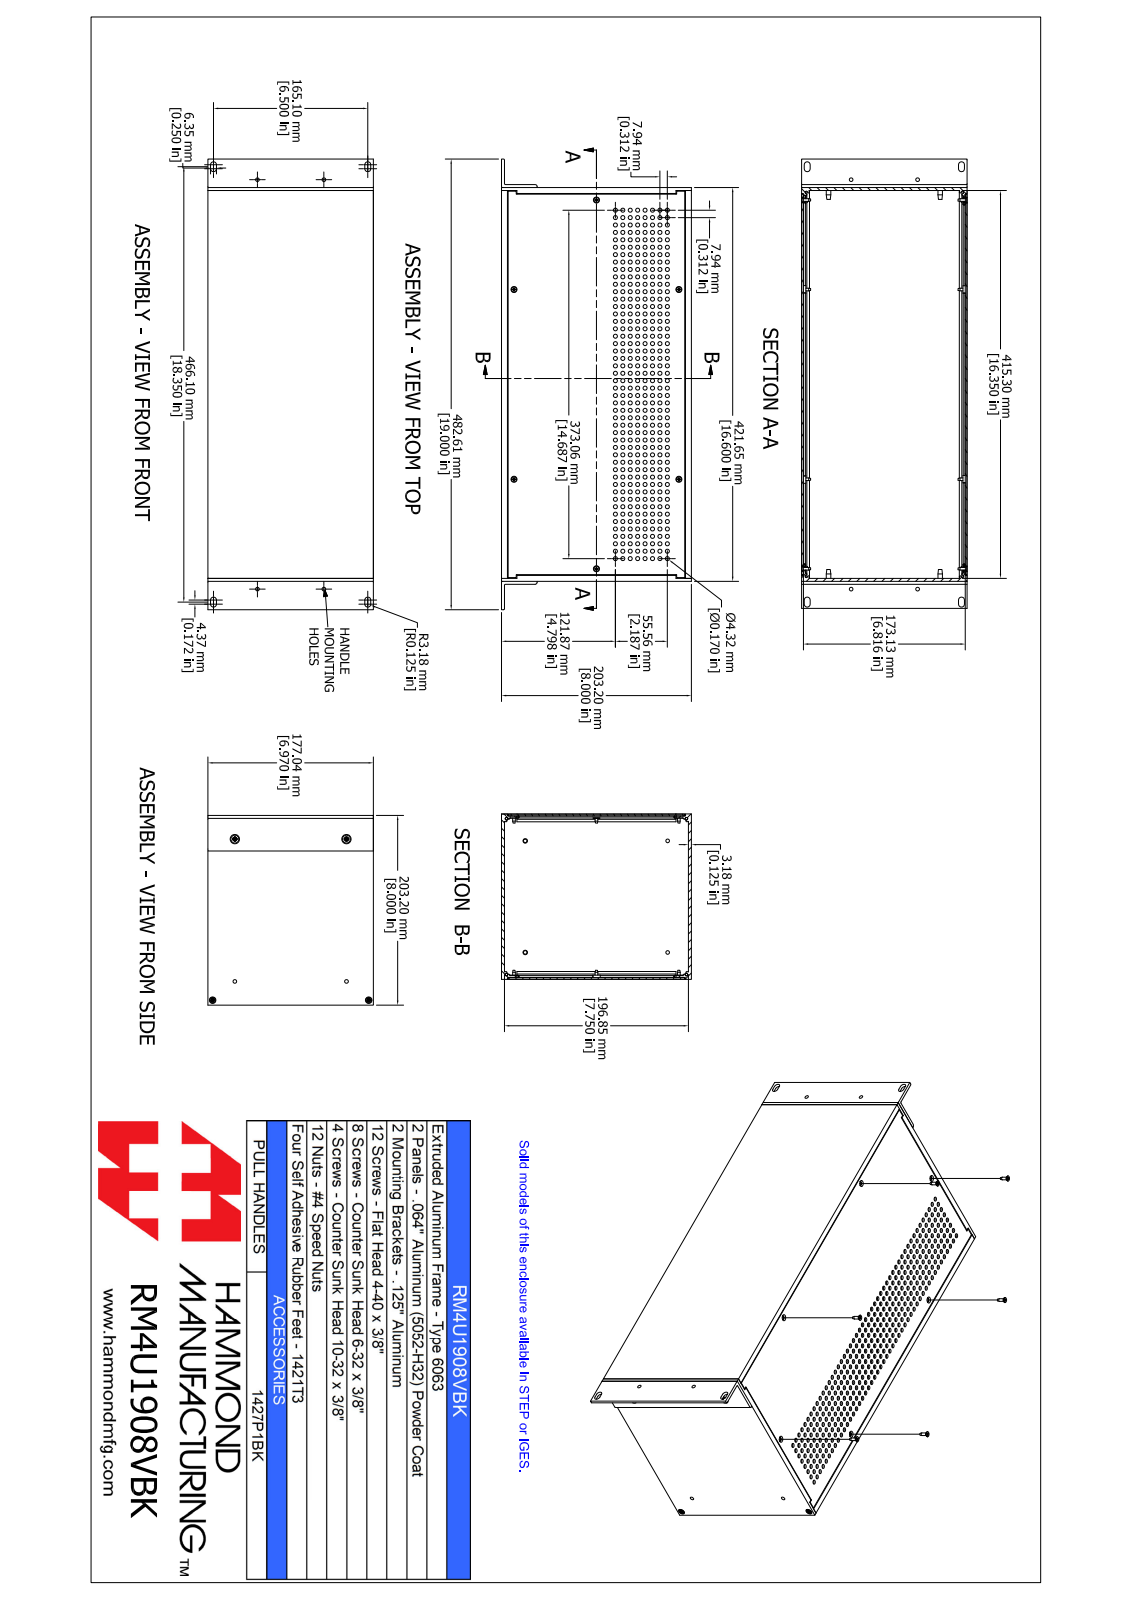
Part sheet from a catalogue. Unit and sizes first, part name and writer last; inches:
Units: inches
Overall size (bounding box): 19 × 8 × 6.971
Round holes (diameter × count): ⌀0.17 ×384, ⌀0.169 ×8, ⌀0.098 ×6, ⌀0.157 ×6, ⌀0.138 ×4, ⌀0.156 ×4, ⌀0.157 ×4, ⌀0.165 ×2, ⌀0.197 ×2
Round bosses / shafts (diameter × count): ⌀0.214 ×8, ⌀0.112 ×8, ⌀0.238 ×4, ⌀0.138 ×4, ⌀0.333 ×2, ⌀0.19 ×2
Partial cylindrical surfaces — rounded edges, fillets, slot ends (radius × count): R0.039 ×18, R0.015 ×16, R0.038 ×16, R0.049 ×12, R0.055 ×8, R0.125 ×8, R0.131 ×8, R0.079 ×2
Main face-to-face distances: 0.125, 0.071, 6.887, 7.875, 8, 6.816, 6.957, 16.475, 7.75, 16.6
Hole centre spacings: 0.699, 0.313, 0.625, 0.988, 1.289, 0.312, 0.442, 0.698
Volume: 68.75 in³ · Surface area: 1 381 in²
Bodies: 44 solids, 1972 faces (564 planar, 976 cylindrical, 432 other)
Part name (STEP PRODUCT): RM4U1908VBK
STEP written by: SolidWorks 2021 (AUTOMOTIVE_DESIGN)
